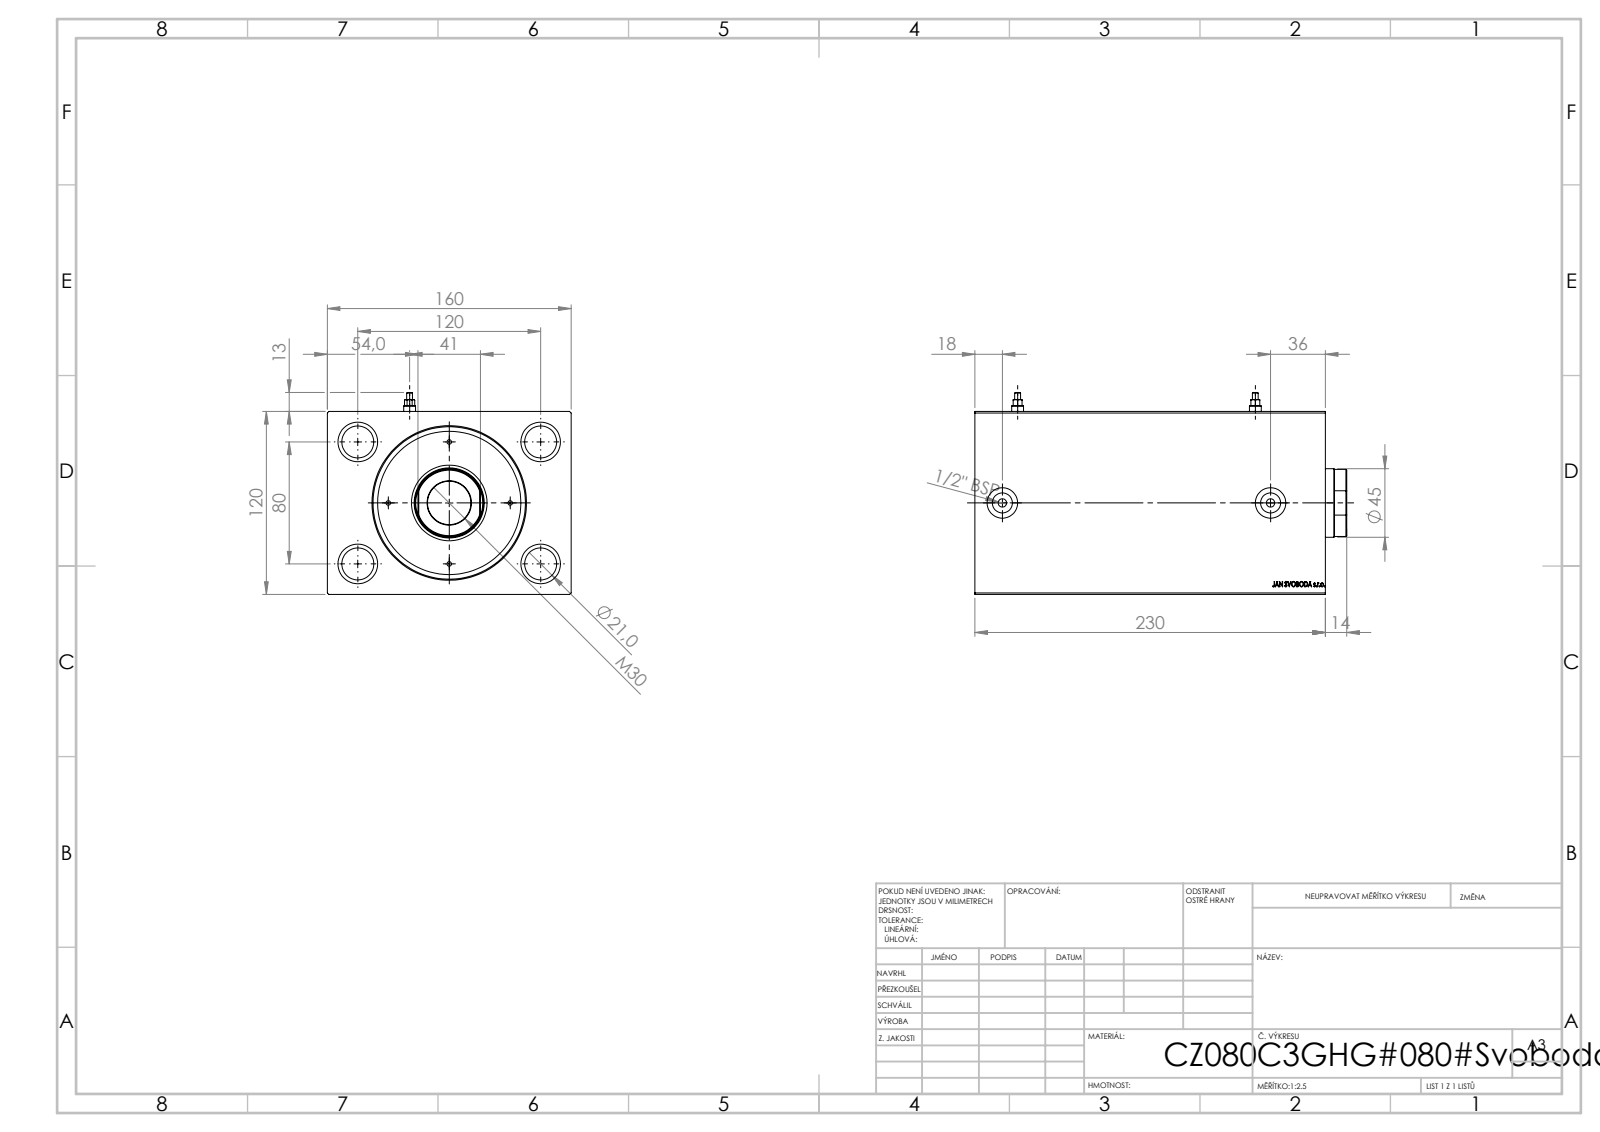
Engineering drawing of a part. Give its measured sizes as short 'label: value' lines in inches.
written by: SolidWorks 2019 (CONFIG_CONTROL_DESIGN)
unit: in
bodies: 1 solid, 825 faces (397 planar, 46 cylindrical, 382 other)
size: 9.055 × 6.299 × 4.724
volume: 183.6 in³; area: 433.5 in²
holes: 4× ⌀0.827, 4× ⌀1.024, 2× ⌀0.217, 2× ⌀0.315, 2× ⌀0.518, 2× ⌀0.787, 1× ⌀1.417, 1× ⌀3.15, 1× ⌀3.937
face distances: 4.724, 6.299, 9.055, 8.059, 0.996, 0.551, 7.508, 8.504, 0.407, 8.648
hole spacings: 2.839, 3.15, 4.724, 5.678, 6.142, 6.929
